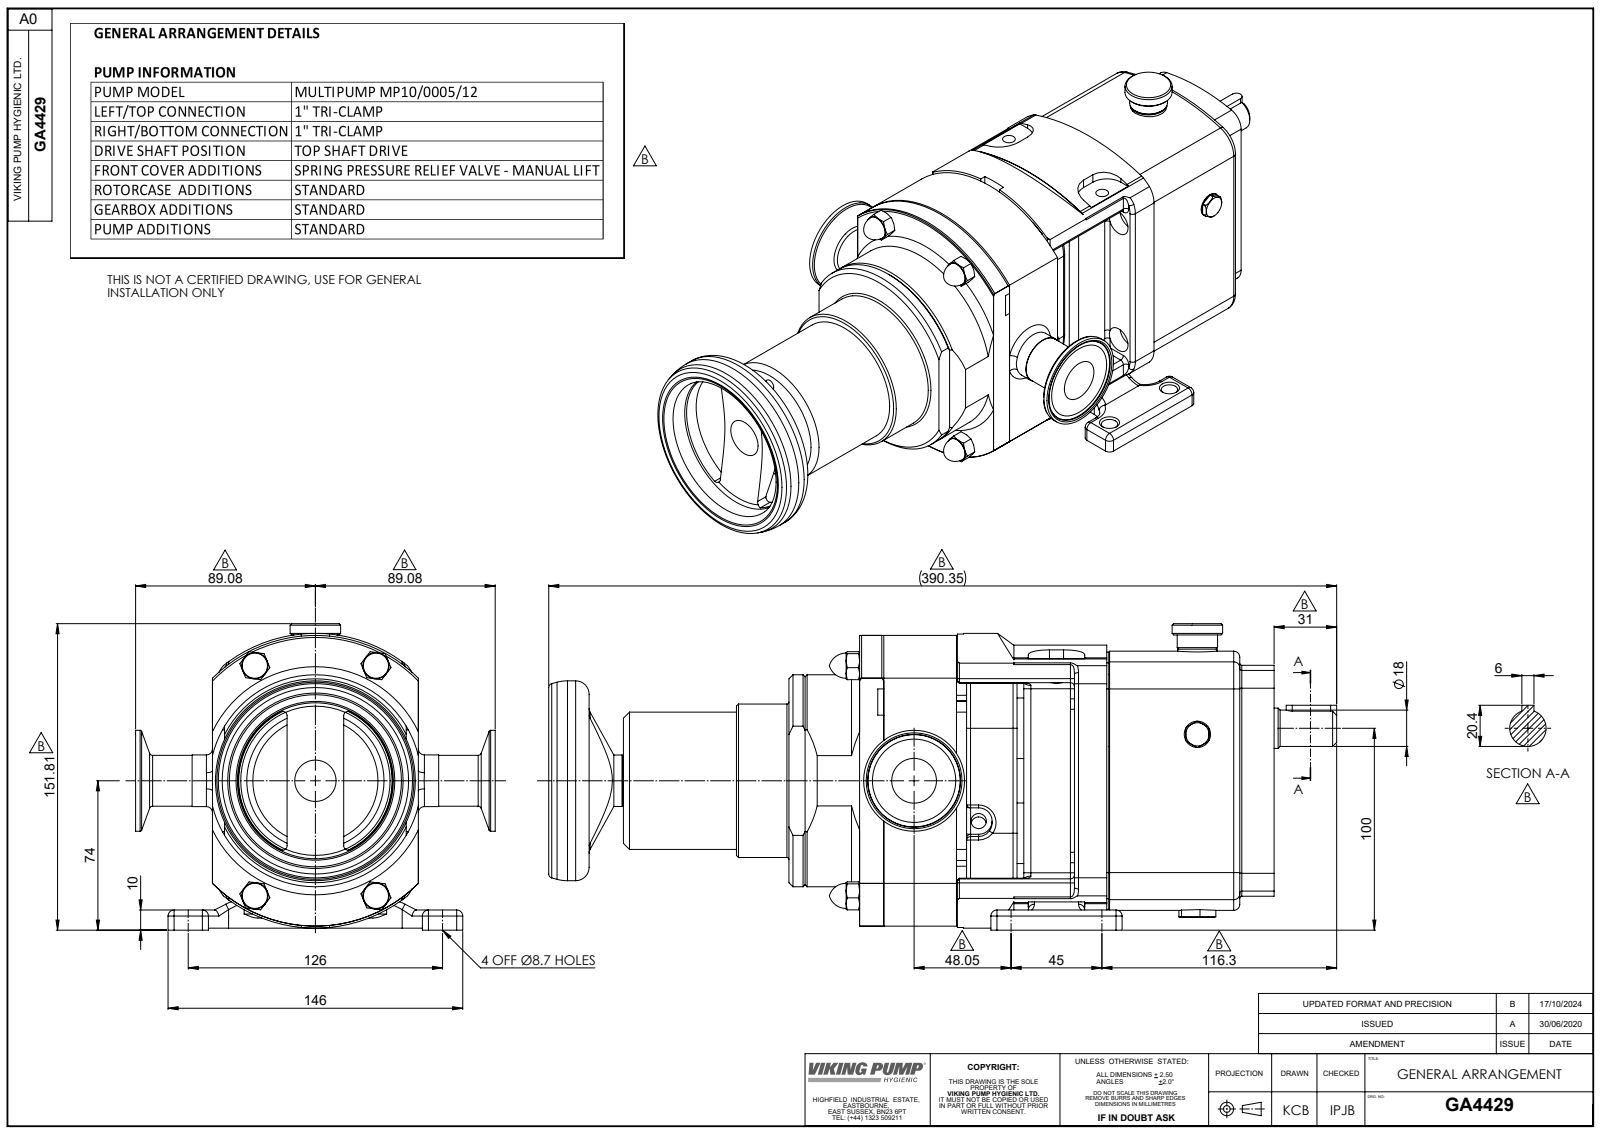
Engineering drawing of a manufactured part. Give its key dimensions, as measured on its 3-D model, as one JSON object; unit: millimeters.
{"part_name": "MP-CP10 SPRING PRV; GA4429; Copy of Spoked handwheels VRTP.100 A-10^MP-CP10 SPRING PRV With Handwheel; Z94-5121-11 - 1 INCH v2 (+2 more)", "step_written_by": "SolidWorks 2023 (AUTOMOTIVE_DESIGN)", "units": "millimeters", "bodies": {"solids": 5, "faces": 772, "planar": 246, "cylindrical": 247, "other": 279}, "overall_size": [390.35, 178.15, 151.81], "volume_mm3": 3103000, "surface_area_mm2": 261250, "round_holes": [[8.7, 4], [14, 4], [6, 2], [6.8, 2], [7.63, 2], [10, 1], [22.2, 1], [22.3, 1], [22.53, 1]], "round_bosses_or_shafts": [[30, 2], [105, 1], [99, 1], [76, 1], [68, 1], [50, 1], [25.6, 1], [25.5, 1]], "partial_cylinders_radius": [[2, 30], [3, 26], [13.5, 12], [10.5, 8], [3.5, 6], [2.2, 4], [5.5, 4], [6, 4]], "face_to_face_distances": [5, 12, 97, 193.35, 205.35, 102, 124, 92, 16, 69.35], "hole_center_spacings": [35.92, 100.55, 25, 40.64, 40.65, 45, 54.09, 54.1]}
